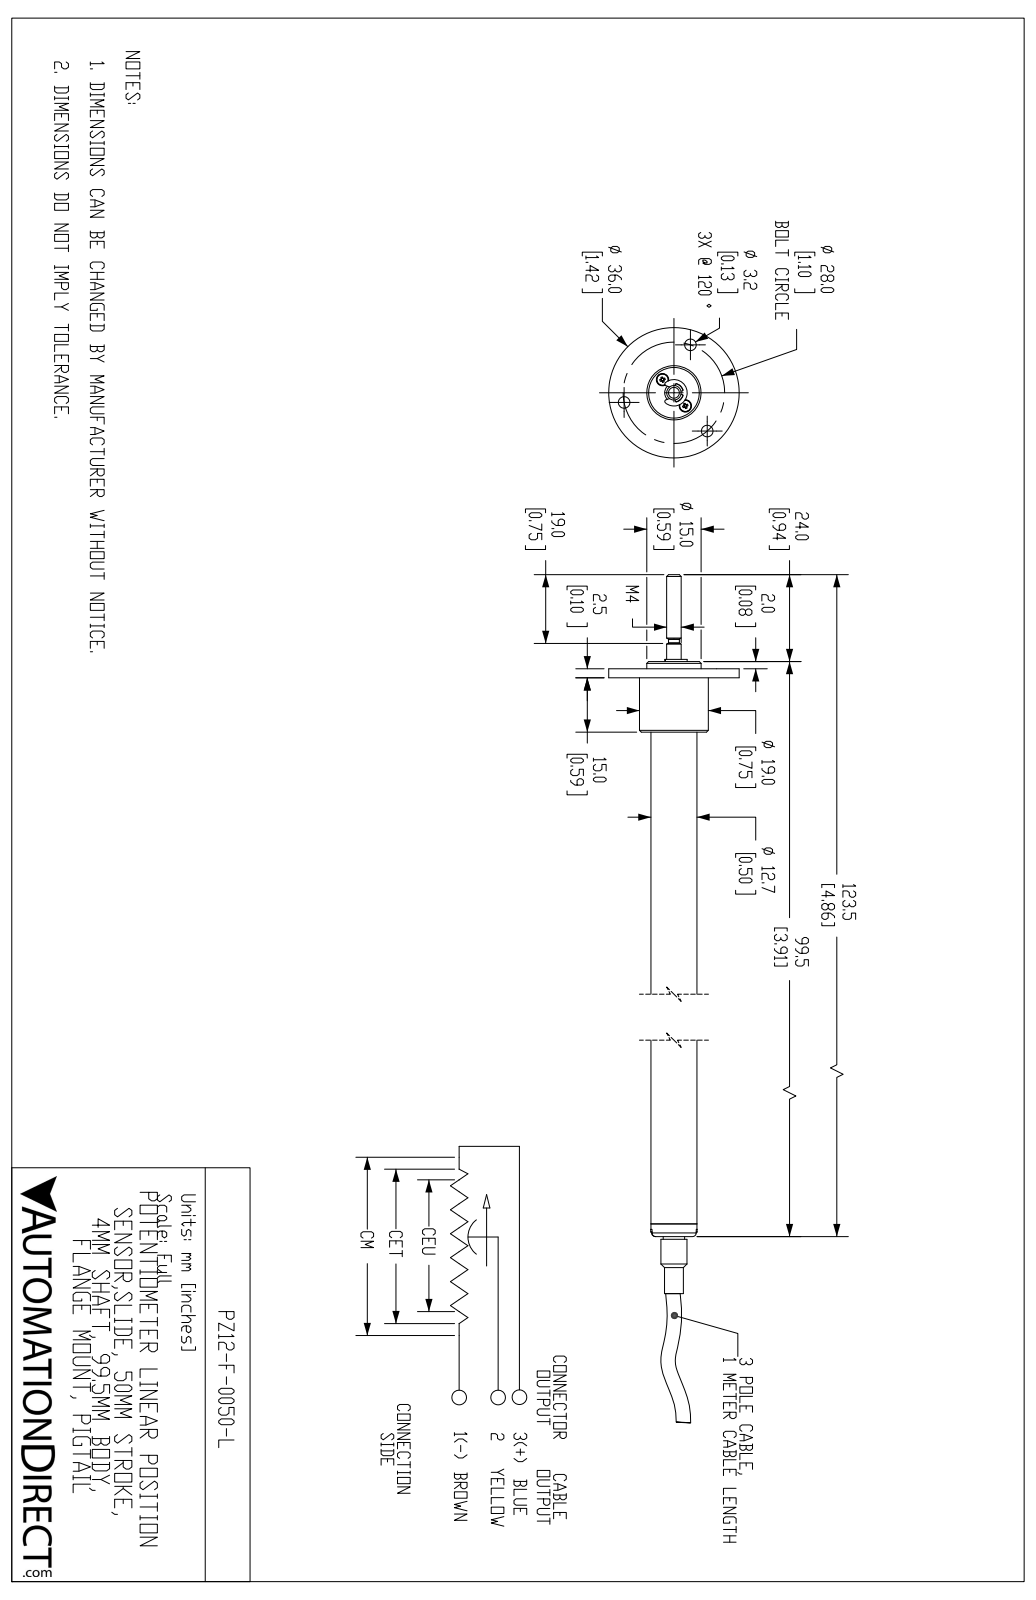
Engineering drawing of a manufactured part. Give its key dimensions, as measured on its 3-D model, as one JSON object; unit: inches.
{"part_name": "PZ12-F-0050-L", "step_written_by": "SolidWorks 2019 (AUTOMOTIVE_DESIGN)", "units": "inches", "bodies": {"solids": 11, "faces": 489, "planar": 129, "cylindrical": 135, "other": 225}, "overall_size": [6.809, 1.417, 1.417], "volume_in3": 1.138, "surface_area_in2": 18.47, "round_holes": [[0.126, 4], [0.055, 2], [0.079, 2], [0.134, 2], [0.039, 1], [0.138, 1], [0.201, 1], [0.236, 1], [0.502, 1]], "round_bosses_or_shafts": [[0.126, 4], [0.063, 4], [1.417, 1], [0.748, 1], [0.591, 1], [0.5, 1], [0.283, 1], [0.233, 1]], "partial_cylinders_radius": [[0.01, 4], [0.02, 2], [0.026, 2], [0.069, 2], [0.017, 1], [0.103, 1], [0.144, 1]], "face_to_face_distances": [0.098, 3.524, 3.622, 0.079, 3.701, 0.177, 0.591, 2.933, 0.689, 0.768], "hole_center_spacings": [0.189, 0.551, 0.076, 0.37, 0.485, 0.666, 0.955, 0.362]}
